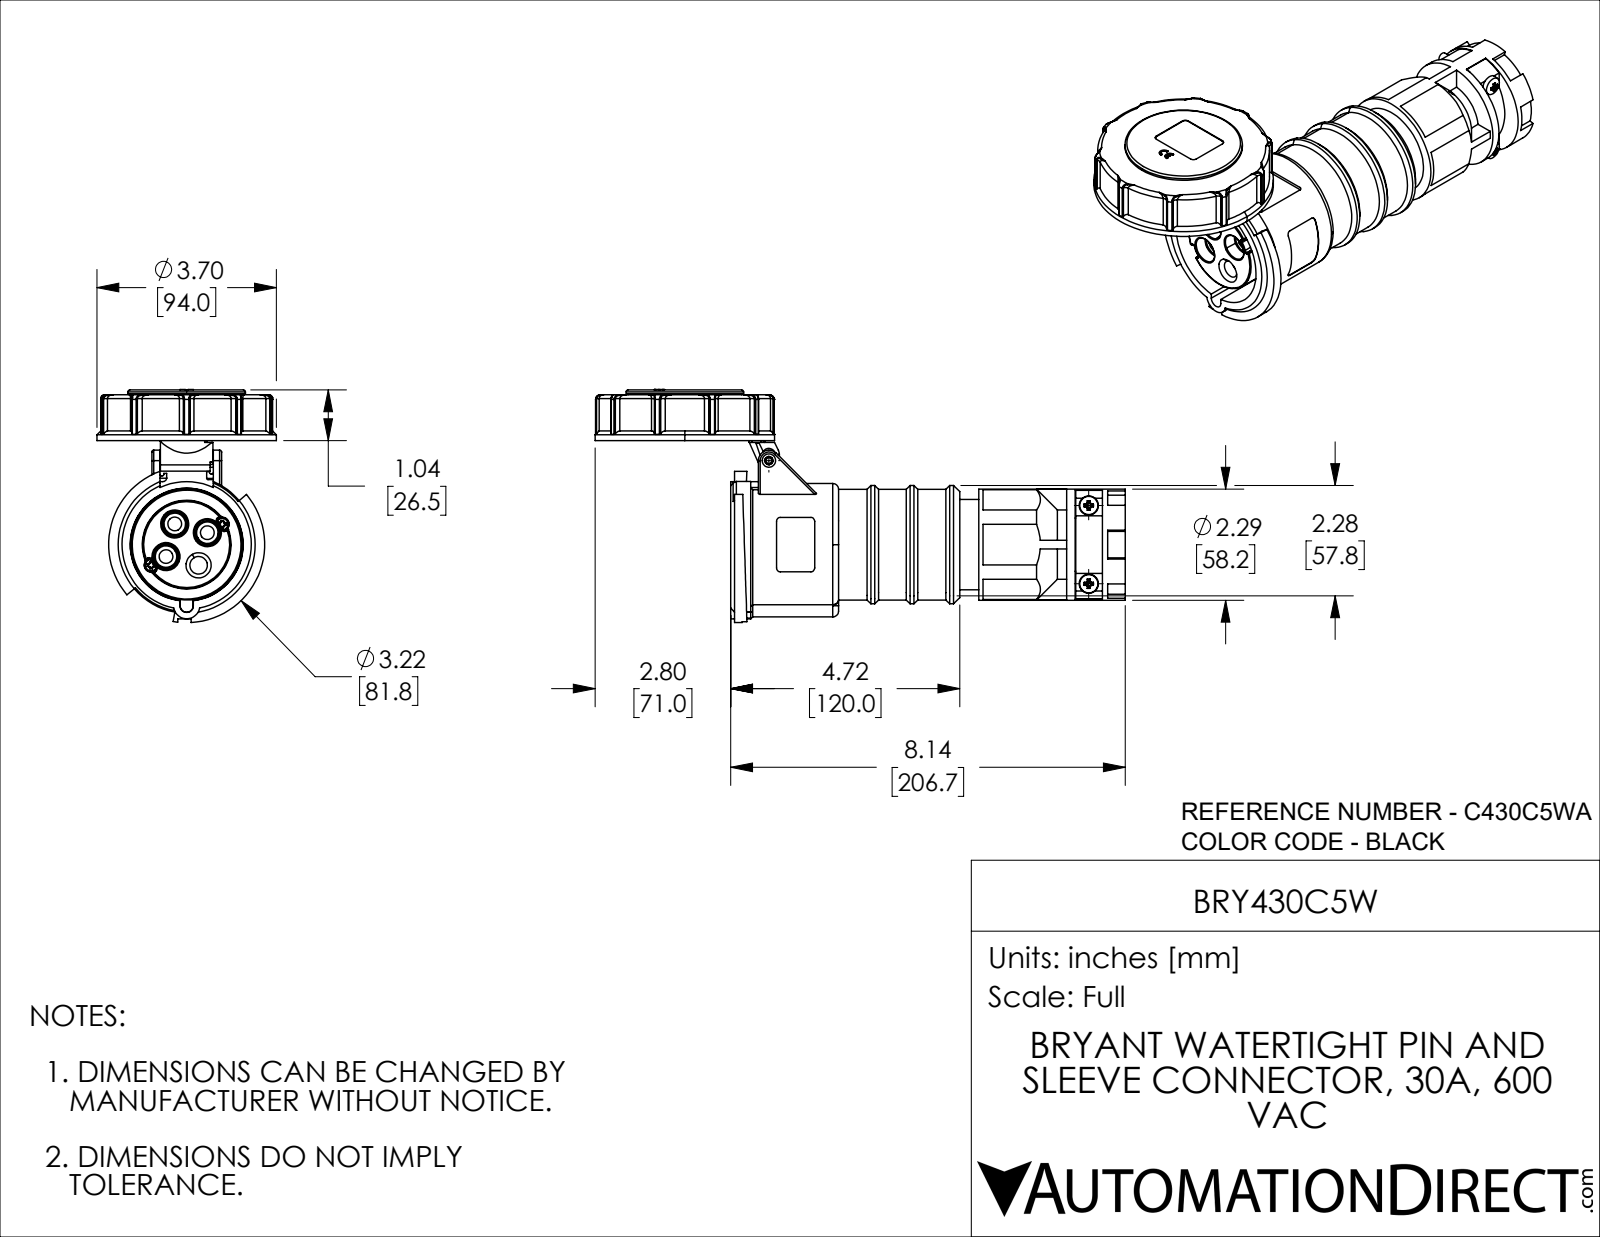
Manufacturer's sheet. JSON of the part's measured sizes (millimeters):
{"part_name": "BRY430C5W", "step_written_by": "SolidWorks 2021 (CONFIG_CONTROL_DESIGN)", "units": "millimeters", "bodies": {"solids": 12, "faces": 958, "planar": 319, "cylindrical": 314, "other": 325}, "overall_size": [277.7, 122.01, 94], "volume_mm3": 592472, "surface_area_mm2": 120195, "round_holes": [[7.2, 5], [5, 2], [3, 1], [4.3, 1], [7, 1], [9.2, 1], [29.5, 1], [36.5, 1], [46.5, 1], [49.04, 1], [84, 1]], "round_bosses_or_shafts": [[94, 1], [71.75, 1], [64, 1], [62, 1], [61.5, 1], [59.5, 1], [58.2, 1], [58, 1]], "partial_cylinders_radius": [[2.5, 24], [0.5, 23], [1, 11], [2, 10], [0.75, 5], [1.25, 4], [1.75, 4], [3.4, 2]], "face_to_face_distances": [4.5, 21, 2.5, 64.7, 18.7, 10, 23.5, 46, 54.2, 23.2], "hole_center_spacings": [12.5, 17.68, 24.87, 9, 21.5, 25.01, 34, 41]}
